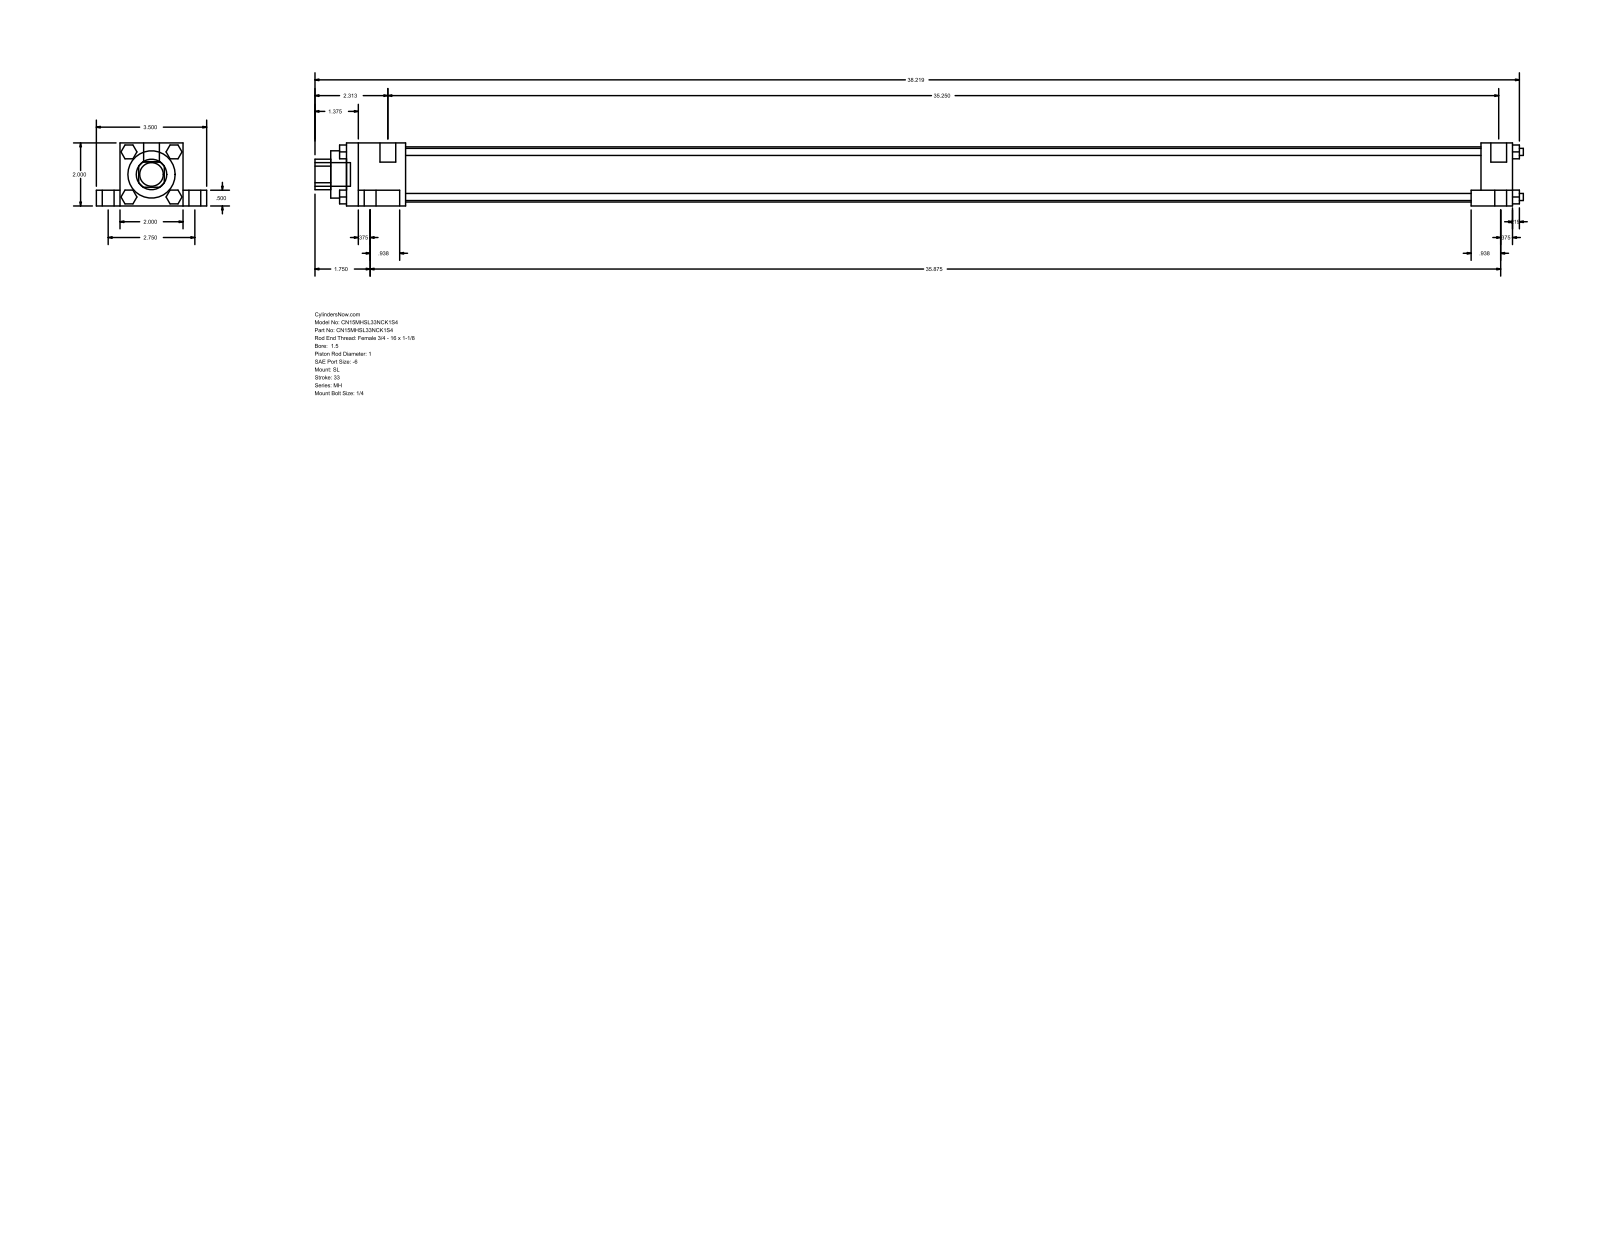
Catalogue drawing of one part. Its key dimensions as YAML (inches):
part_name: "MH_SL__0150_1"
step_written_by: "GSSL Pune (CONFIG_CONTROL_DESIGN)"
units: inches
bodies: {solids: 0, faces: 148, planar: 112, cylindrical: 36, other: 0}
overall_size: [38.344, 3.5, 2]
round_holes:
  - {diameter: 1, count: 1}
  - {diameter: 1.5, count: 1}
  - {diameter: 1.75, count: 1}
round_bosses_or_shafts:
  - {diameter: 0.625, count: 4}
  - {diameter: 0.375, count: 4}
  - {diameter: 0.225, count: 4}
  - {diameter: 0.219, count: 4}
  - {diameter: 0.5, count: 2}
  - {diameter: 0.75, count: 1}
partial_cylinders:
  - {radius: 0.484, count: 1}
face_to_face_distances: [2, 0.5, 1.5, 0.75, 2.75, 37, 1, 0.375, 1.313, 35.313]
